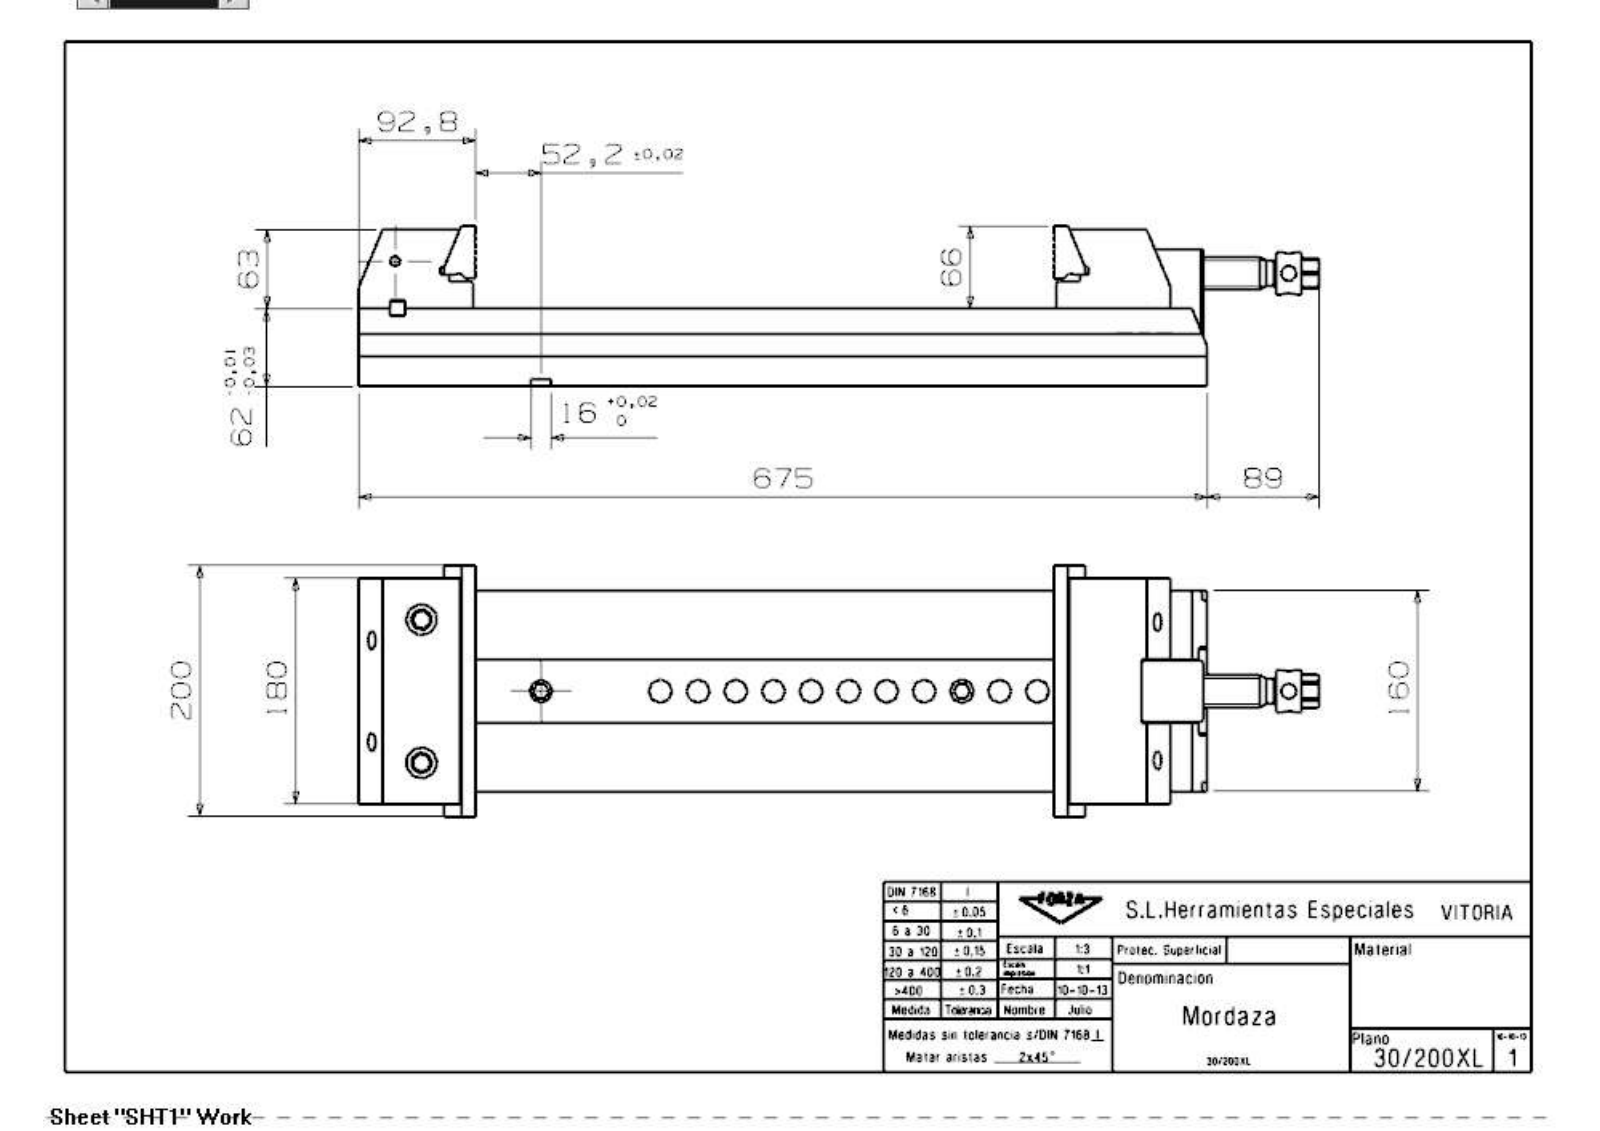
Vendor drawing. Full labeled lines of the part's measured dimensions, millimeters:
Part name (STEP PRODUCT): 30_200XL_Mordaza
STEP written by: SIEMENS PLM Software NX 7.5 (CONFIG_CONTROL_DESIGN)
Units: millimetres
Bodies: 12 solids, 471 faces (277 planar, 136 cylindrical, 58 other)
Overall size (bounding box): 764 × 200 × 127.95
Volume: 7 121 000 mm³ · Surface area: 715 058 mm²
Round holes (diameter × count): ⌀15 ×6, ⌀5.19 ×5, ⌀13 ×5, ⌀6.99 ×4, ⌀8.5 ×4, ⌀10 ×4, ⌀19 ×4, ⌀8.78 ×3, ⌀10.58 ×3, ⌀12 ×2, ⌀12.38 ×2, ⌀14.38 ×2
Round bosses / shafts (diameter × count): ⌀34 ×1, ⌀33.8 ×1, ⌀26 ×1, ⌀20 ×1, ⌀16.5 ×1
Partial cylindrical surfaces — rounded edges, fillets, slot ends (radius × count): R0.4 ×24, R1.5 ×4, R8 ×4, R20 ×4, R1.6 ×2, R6 ×2, R7 ×2, R4 ×1
Main face-to-face distances: 62, 29.6, 32.4, 125, 160, 2, 27.6, 60, 7.5, 152.5
Hole centre spacings: 14.5, 95.5, 81, 110, 16.47, 16.55, 30, 30.27
